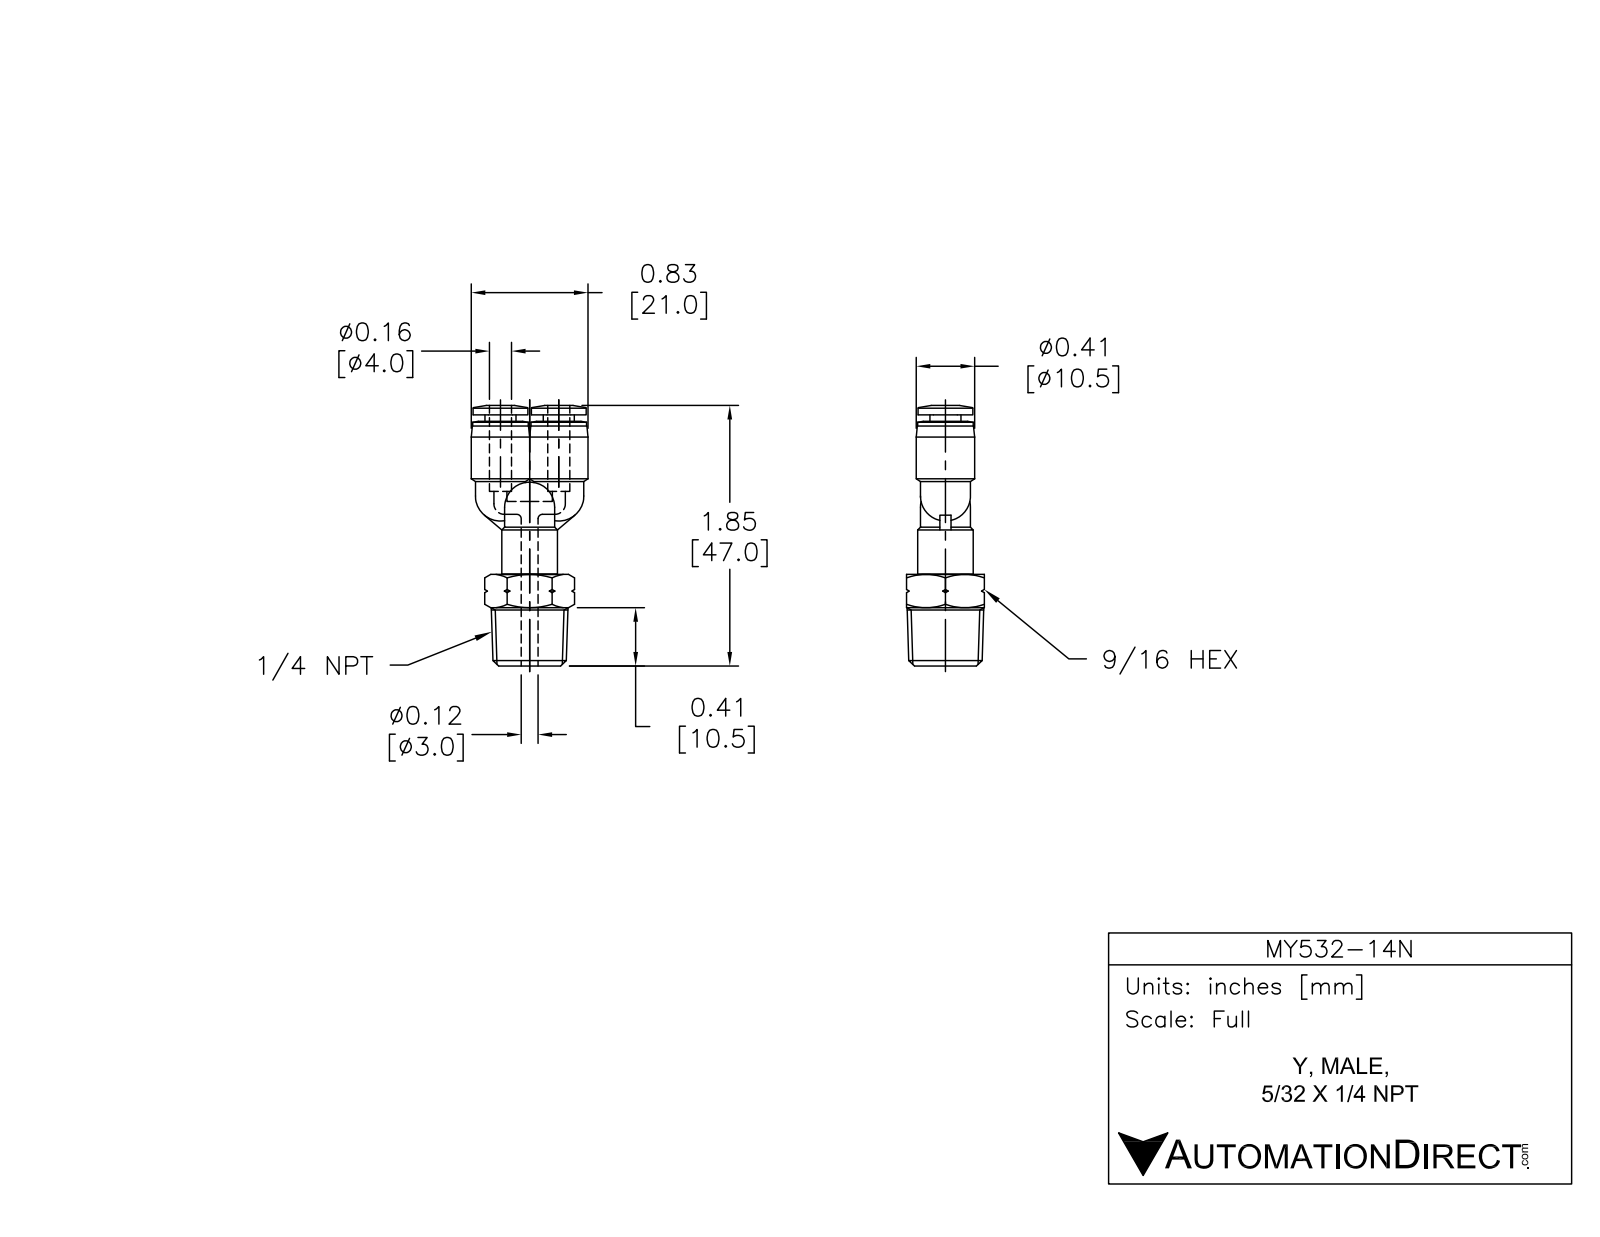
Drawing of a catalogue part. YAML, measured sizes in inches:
part_name: "MY532-14N"
step_written_by: "SolidWorks 2015 (AUTOMOTIVE_DESIGN)"
units: inches
bodies: {solids: 1, faces: 128, planar: 22, cylindrical: 31, other: 75}
overall_size: [1.846, 0.827, 0.551]
volume: 0.34
surface_area: 5.527
round_holes:
  - {diameter: 0.169, count: 2}
  - {diameter: 0.118, count: 1}
round_bosses_or_shafts:
  - {diameter: 0.394, count: 3}
  - {diameter: 0.354, count: 3}
  - {diameter: 0.413, count: 2}
  - {diameter: 0.388, count: 2}
  - {diameter: 0.22, count: 2}
face_to_face_distances: [0.551, 1.78, 0.65, 1.13, 1.734, 1.085, 0.045, 0.236, 0.315, 1.236]
hole_center_spacings: [0.207, 0.413]
